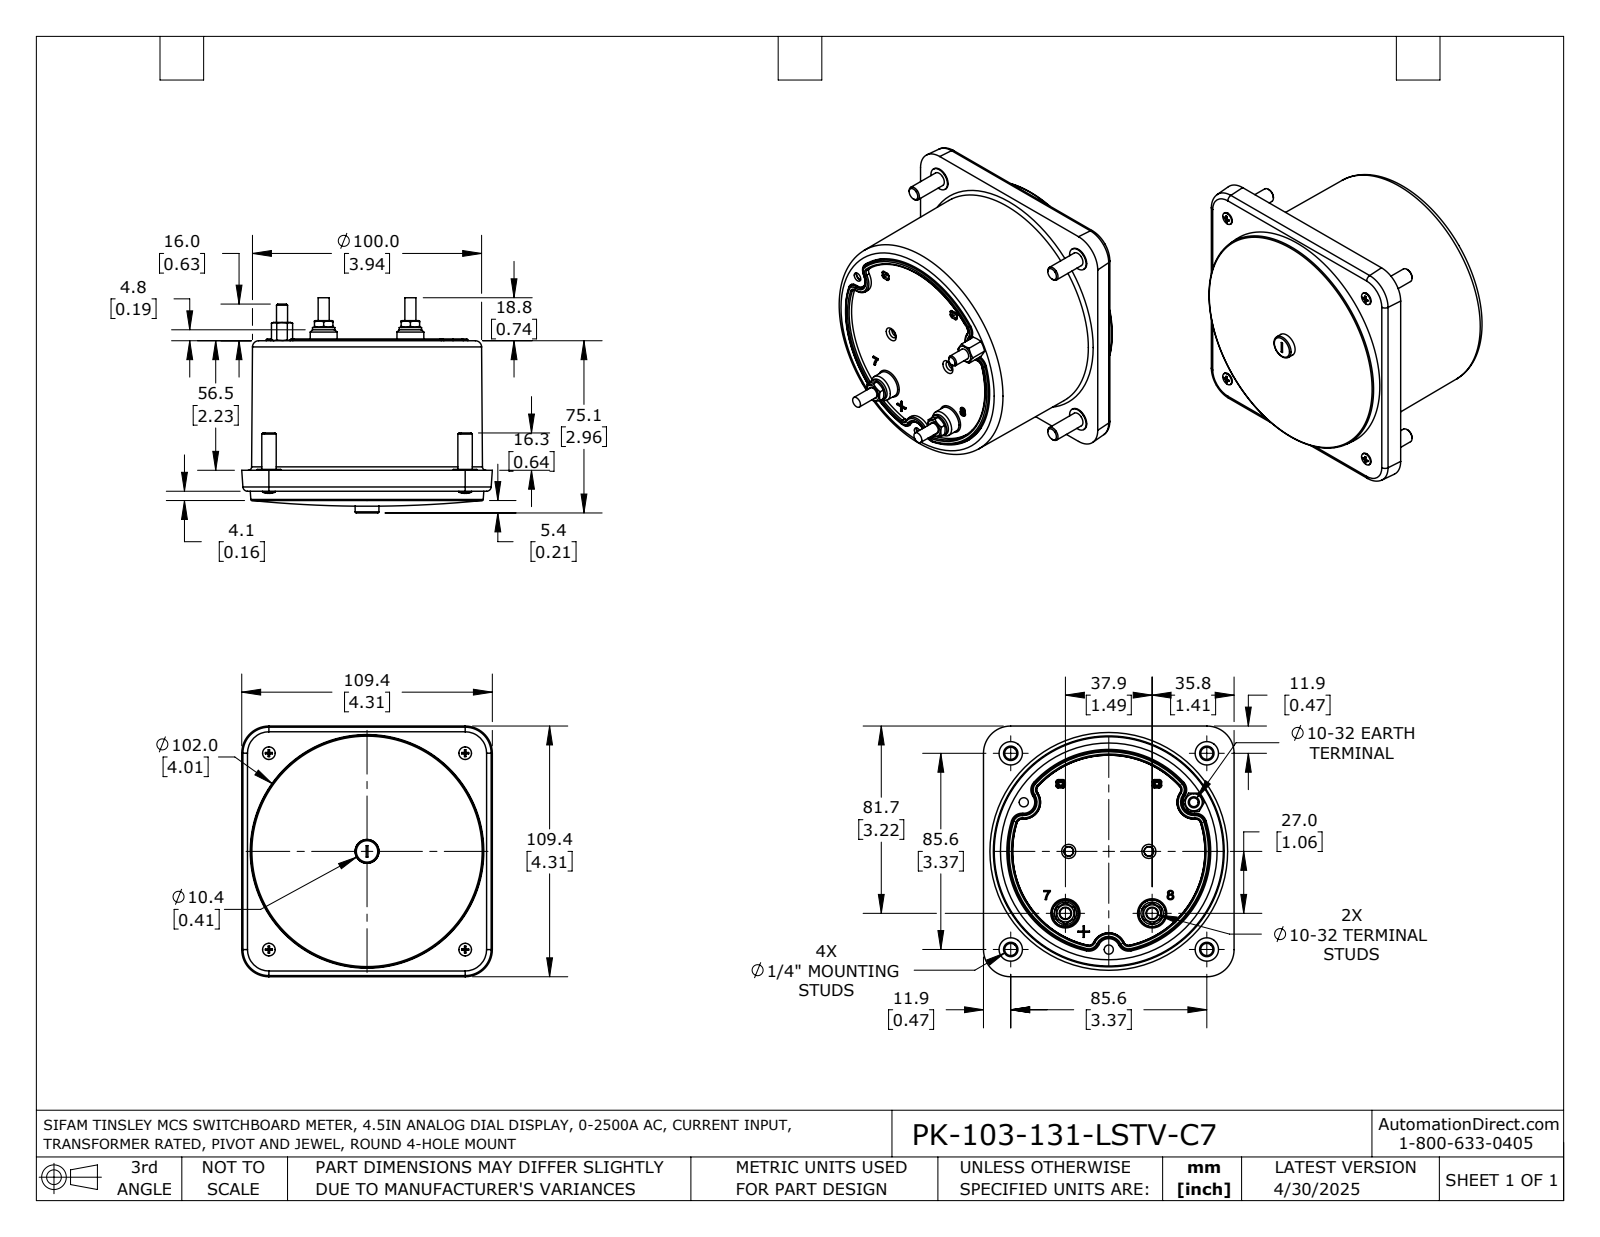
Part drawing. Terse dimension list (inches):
name: PK-103-131-LSTV-C7
written by: SolidWorks 2021 (AUTOMOTIVE_DESIGN)
unit: in
bodies: 1 solid, 609 faces (167 planar, 141 cylindrical, 301 other)
size: 4.307 × 4.307 × 3.697
volume: 36.28 in³; area: 82.21 in²
holes: 4× ⌀0.094, 4× ⌀0.138, 4× ⌀0.315, 3× ⌀0.157, 2× ⌀0.209
bosses: 4× ⌀0.402, 4× ⌀0.248, 4× ⌀0.217, 4× ⌀0.114, 3× ⌀0.19, 2× ⌀0.384, 1× ⌀0.146
rounds: 24× R0.02, 9× R0.189, 4× R0.079, 1× R1.752
face distances: 2.177, 2.537, 0.36, 0.048, 2.225, 2.585, 0.489, 2.715, 2.667, 0.129
hole spacings: 3.372, 3.37, 3.374, 3.378, 3.38, 4.769, 0.971, 1.126
